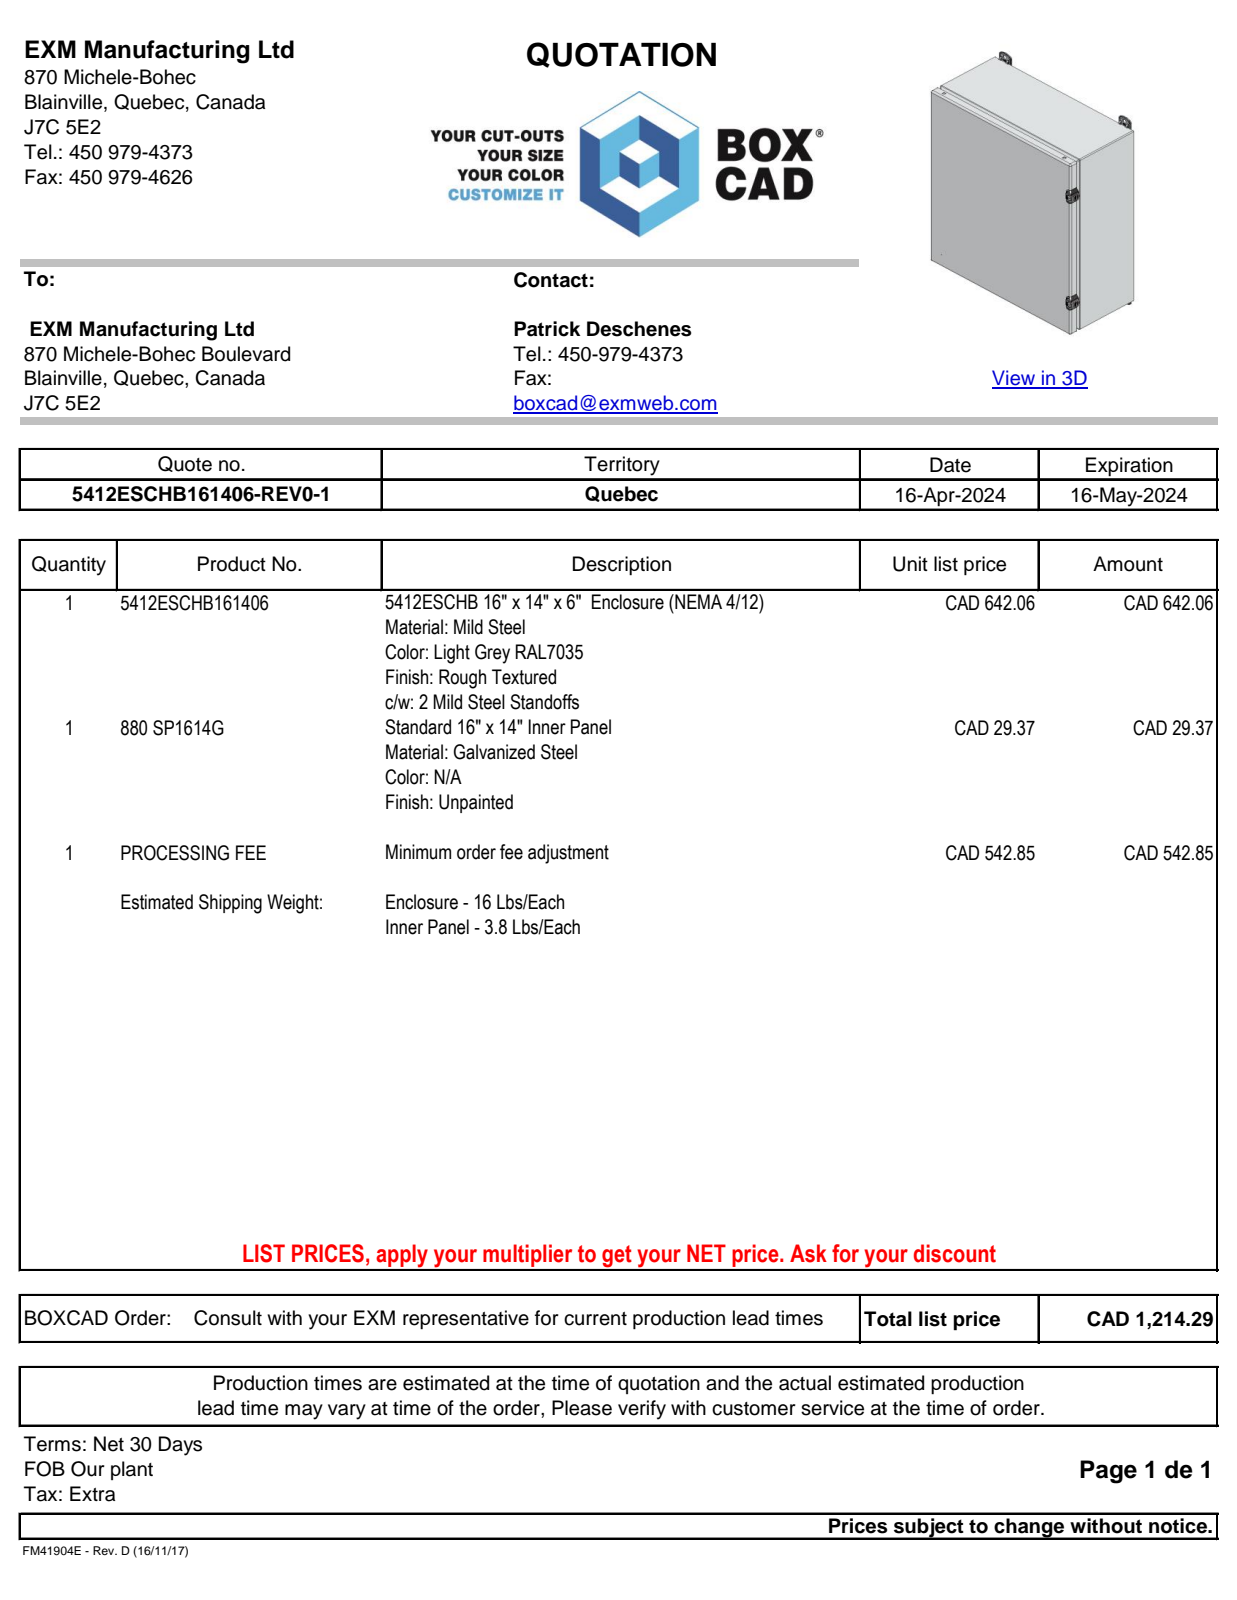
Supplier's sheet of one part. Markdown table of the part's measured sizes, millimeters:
| quantity | value |
| --- | --- |
| part name | 5412ESCHB161406; 5412ESCHB161406B; 5412ESCHB161406B-P; STK-Q-08350 (+8 more) |
| STEP written by | Autodesk Inventor 2024 (AUTOMOTIVE_DESIGN) |
| units | millimeters |
| bodies | 57 solids, 8149 faces (3851 planar, 1834 cylindrical, 2464 other) |
| overall size | 444.4 × 366.8 × 171.1 |
| volume | 1 053 000 mm³ |
| surface area | 1 471 000 mm² |
| round holes (diameter × count) | 5.1 × 11, 0.8 × 6, 6.1 × 6, 7.7 × 4, 7.9 × 4, 8.1 × 4, 4.2 × 2, 4.4 × 2, 4.4 × 2, 5.5 × 2, 6 × 2, 10 × 2 |
| round bosses / shafts (diameter × count) | 5.9 × 8, 0.9 × 6, 13 × 4, 9.9 × 4, 5 × 3, 10.5 × 2, 10 × 2, 8.4 × 2 |
| partial cylindrical surfaces (radius × count) | 0.2 × 226, 0.5 × 179, 0.1 × 98, 1 × 83, 0.3 × 49, 0.3 × 43, 0.6 × 33, 0.8 × 33 |
| main face-to-face distances | 1.3, 163.3, 161.9, 164.6, 13.6, 12.2, 10.5, 11.9, 151.4, 152.8 |
| hole center spacings | 485.6, 13.9, 308.3, 375.4, 330.2, 59.2, 308.9, 311.2 |
